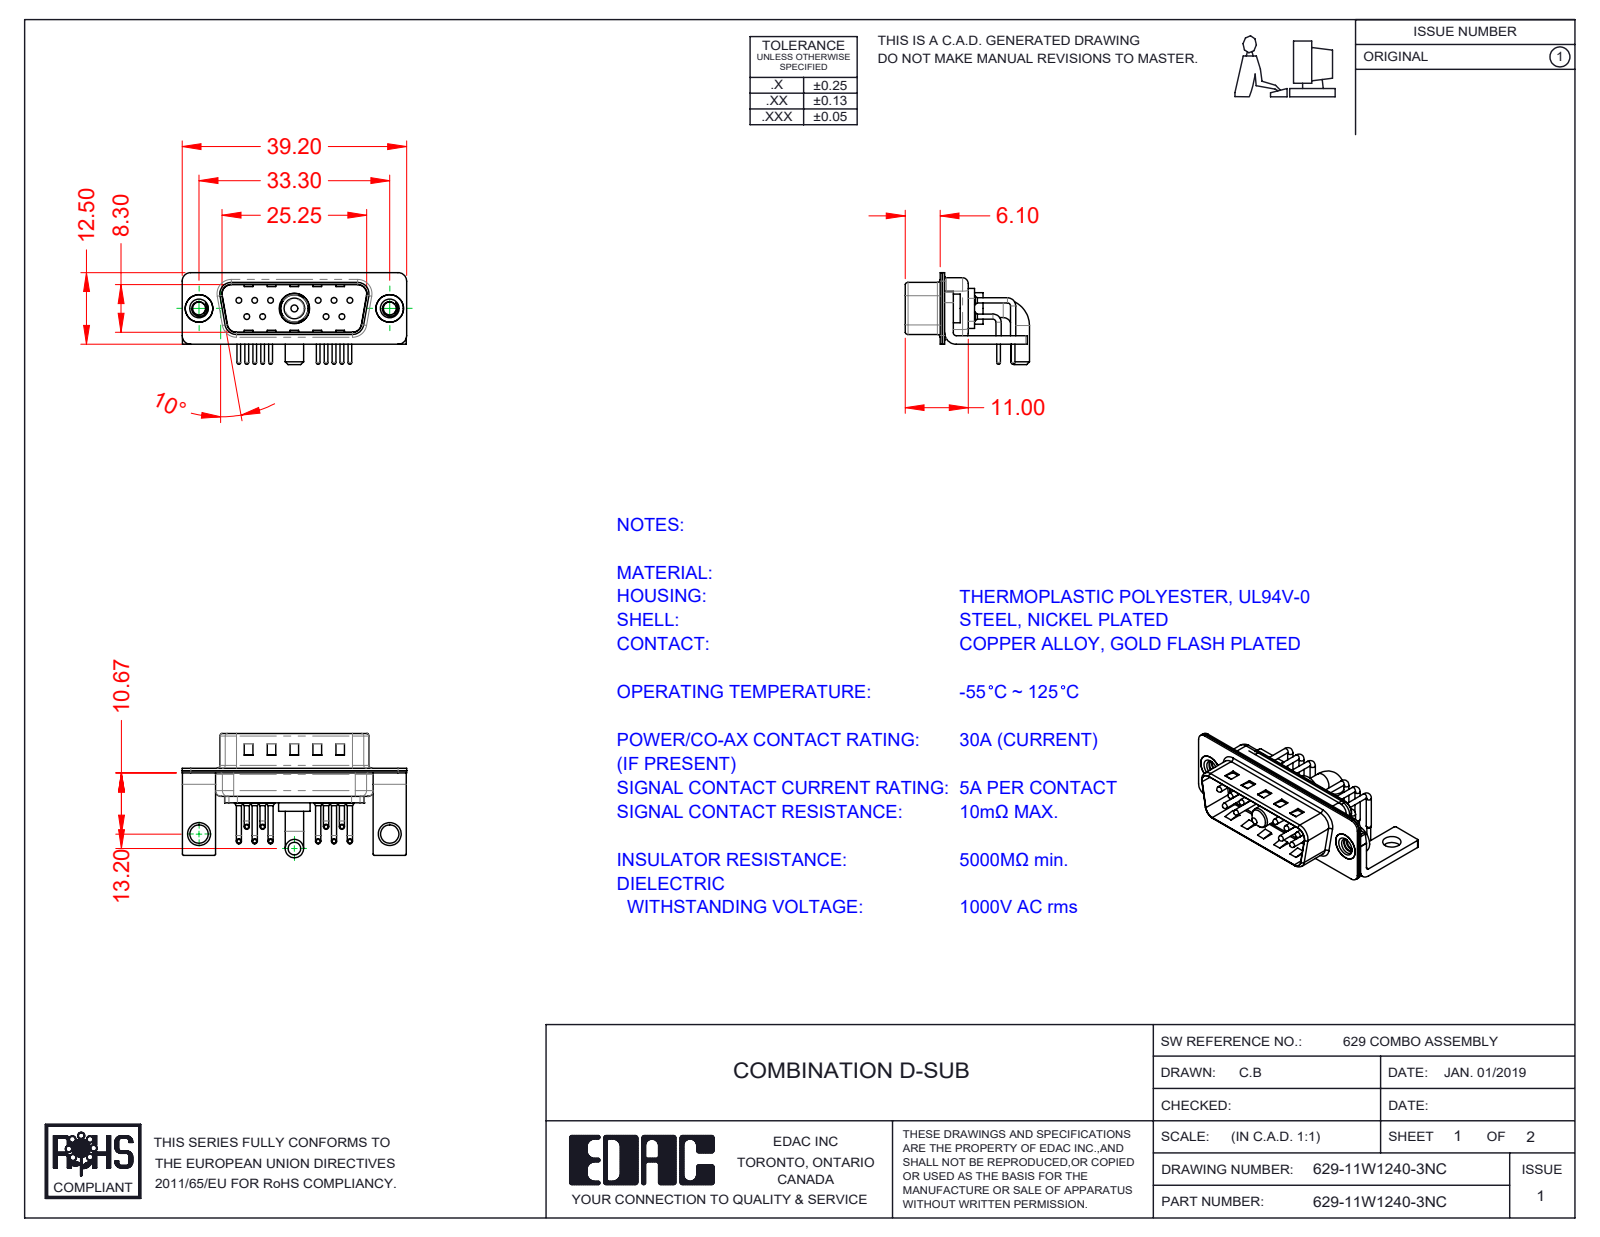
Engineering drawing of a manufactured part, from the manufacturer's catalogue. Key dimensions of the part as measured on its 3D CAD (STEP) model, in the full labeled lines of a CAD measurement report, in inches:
Part name (STEP PRODUCT): 629Combo Contact Row 2; 629Combo Shell Front_15 Contacts; 629Combo Contact Row 1; Power Pin_30A RA (+5 more)
STEP written by: SolidWorks 2020 (CONFIG_CONTROL_DESIGN)
Units: inches
Bodies: 19 solids, 1544 faces (818 planar, 542 cylindrical, 184 other)
Overall size (bounding box): 1.543 × 0.854 × 0.632
Volume: 0.147 in³ · Surface area: 9.136 in²
Round holes (diameter × count): ⌀0.03 ×10, ⌀0.063 ×10, ⌀0.079 ×10, ⌀0.089 ×2, ⌀0.126 ×2, ⌀0.157 ×2, ⌀0.189 ×2, ⌀0.191 ×1, ⌀0.209 ×1
Round bosses / shafts (diameter × count): ⌀0.035 ×20, ⌀0.059 ×10, ⌀0.039 ×10, ⌀0.026 ×10, ⌀0.197 ×2, ⌀0.193 ×2, ⌀0.126 ×2, ⌀0.217 ×1
Partial cylindrical surfaces — rounded edges, fillets, slot ends (radius × count): R0.01 ×16, R0.059 ×16, R0.079 ×13, R0.04 ×10, R0.02 ×9, R0.063 ×8, R0.039 ×7, R0.024 ×4
Main face-to-face distances: 0.016, 0.031, 0.059, 0.374, 0.358, 0.024, 0.343, 0.39, 0.047, 0.205
Hole centre spacings: 0.124, 0.109, 0.545, 0.436, 0.654, 0.198, 0.198, 0.218
